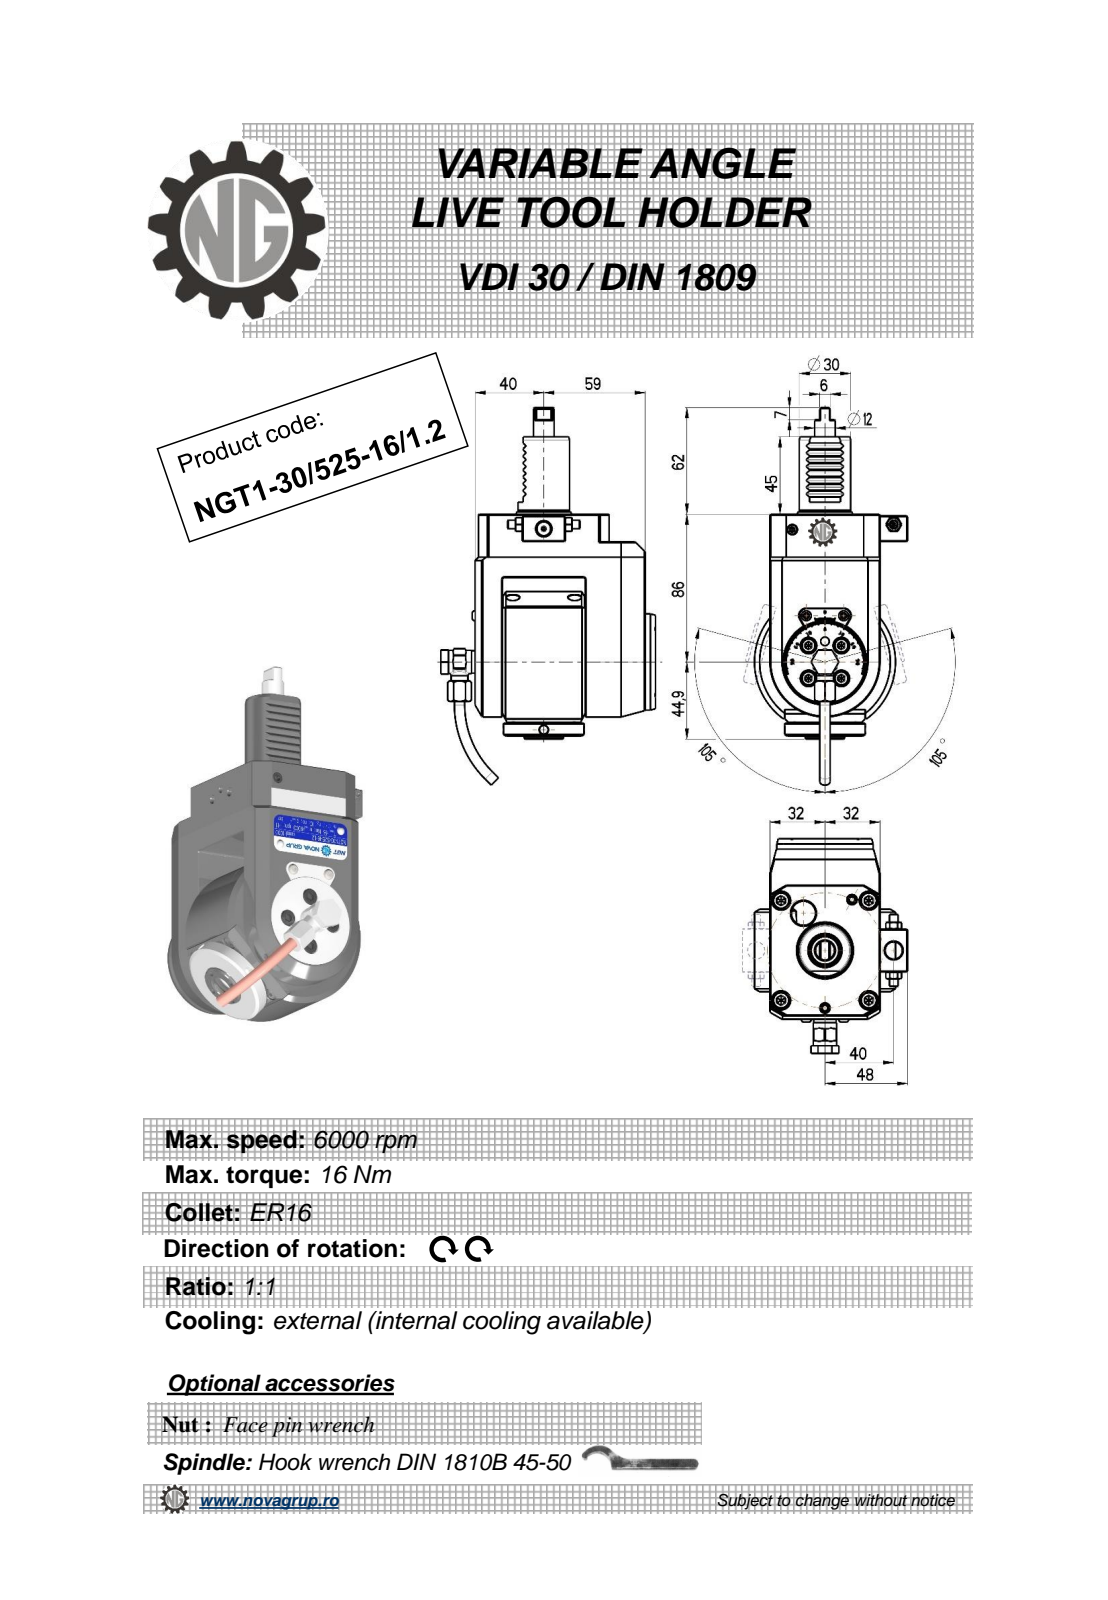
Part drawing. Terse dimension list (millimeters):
name: NGT1_30_525_16_1_2
written by: PRO/ENGINEER BY PARAMETRIC TECHNOLOGY CORPORATION, 2010280 (CONFIG_CONTROL_DESIGN)
unit: mm
bodies: 1 solid, 481 faces (202 planar, 132 cylindrical, 147 other)
size: 219.67 × 124.9 × 89
volume: 753 521 mm³; area: 70 589 mm²
holes: 4× ⌀3.2, 3× ⌀4, 2× ⌀5, 2× ⌀10, 1× ⌀3, 1× ⌀4.2, 1× ⌀6.2, 1× ⌀9, 1× ⌀9.5, 1× ⌀11, 1× ⌀12.5
bosses: 2× ⌀6, 2× ⌀5.7, 1× ⌀82, 1× ⌀56, 1× ⌀47, 1× ⌀35, 1× ⌀30, 1× ⌀23
rounds: 12× R0.26, 8× R0.3, 6× R0.16, 6× R0.5, 2× R1, 1× R7.7, 1× R32
face distances: 64, 16, 37, 99, 6, 105, 35, 21, 14, 83
hole spacings: 9.25, 13.08, 18.5, 41.06, 49.87, 50.26, 0.4, 30.75
